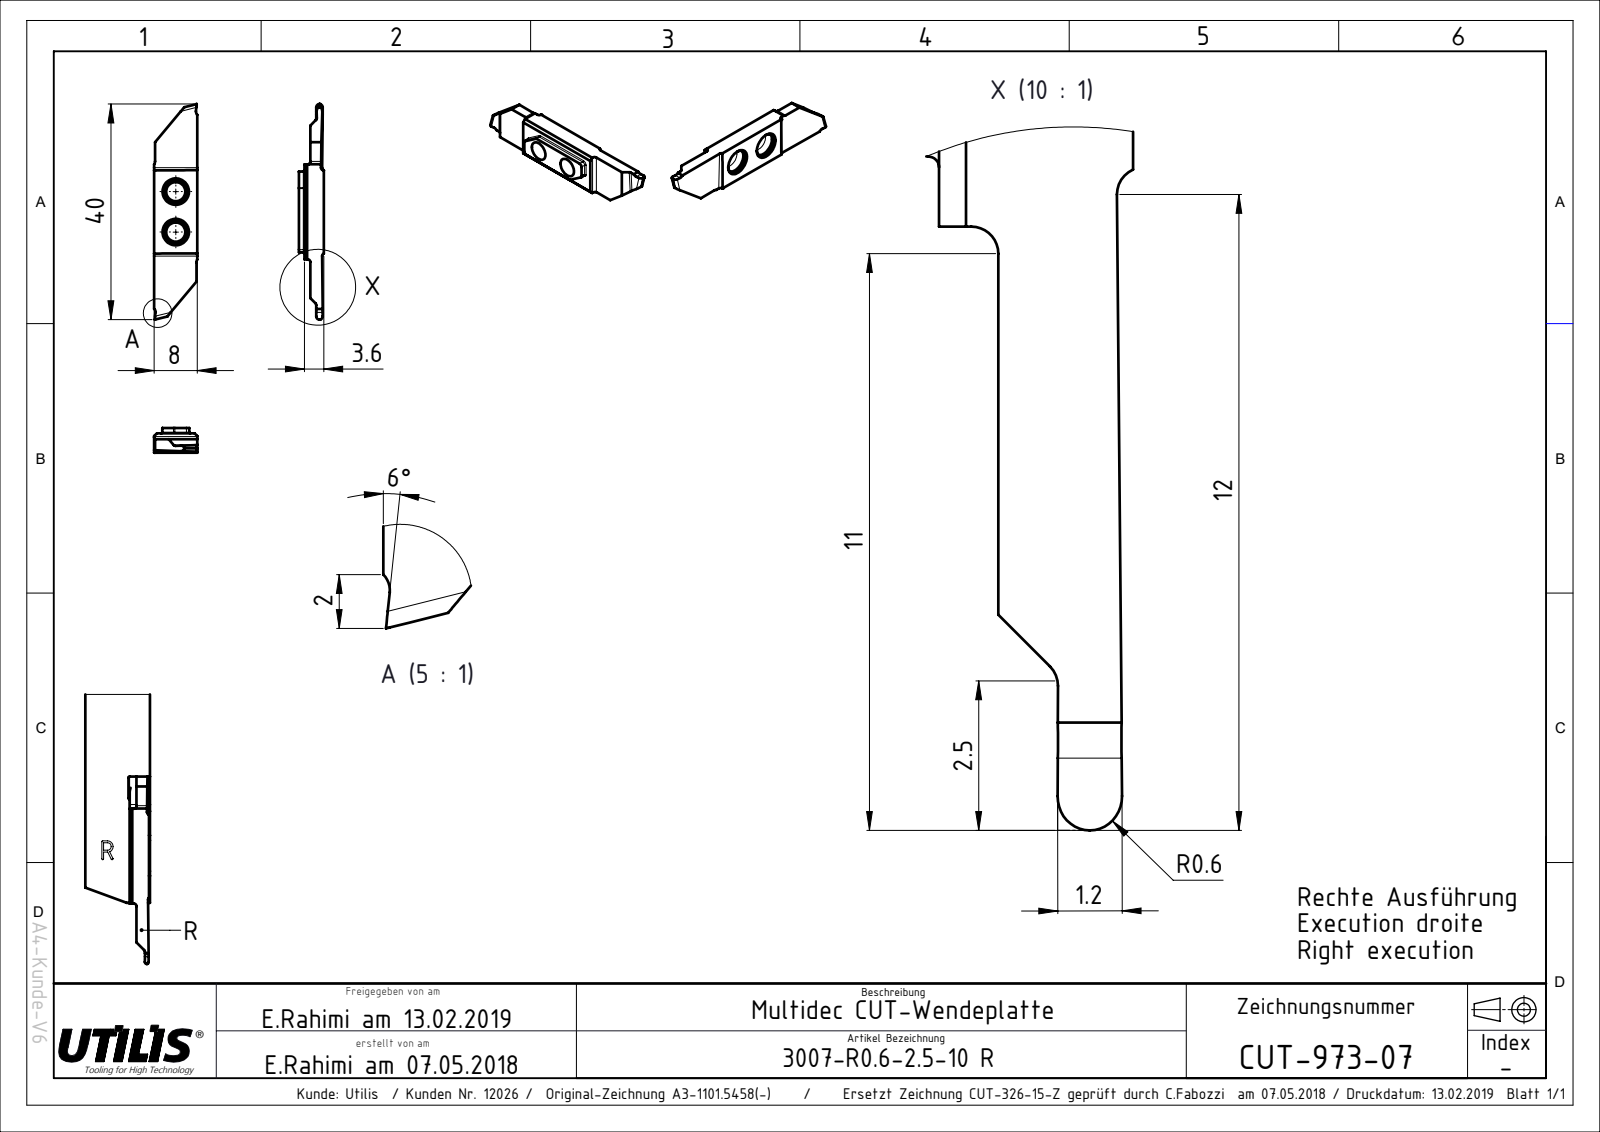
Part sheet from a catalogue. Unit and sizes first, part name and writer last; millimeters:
Units: millimetres
Overall size (bounding box): 43.9 × 20 × 3.6
Round holes (diameter × count): ⌀3.55 ×2
Partial cylindrical surfaces — rounded edges, fillets, slot ends (radius × count): R0.5 ×6, R0.6 ×2, R0.8 ×2, R1 ×2
Main face-to-face distances: 3.6, 1.1, 2.5, 8, 7.85, 22.54, 0.86, 7.7, 17.6, 7.58
Hole centre spacings: 7.5
Volume: 702 mm³ · Surface area: 820 mm²
Bodies: 1 solid, 41 faces (23 planar, 18 cylindrical, 0 other)
Part name (STEP PRODUCT): CUT-973; ASME Y14.5
STEP written by: FormatWorks Professional (AP242_MANAGED_MODEL_BASED_3D_ENGINEERING_MIM_LF)
